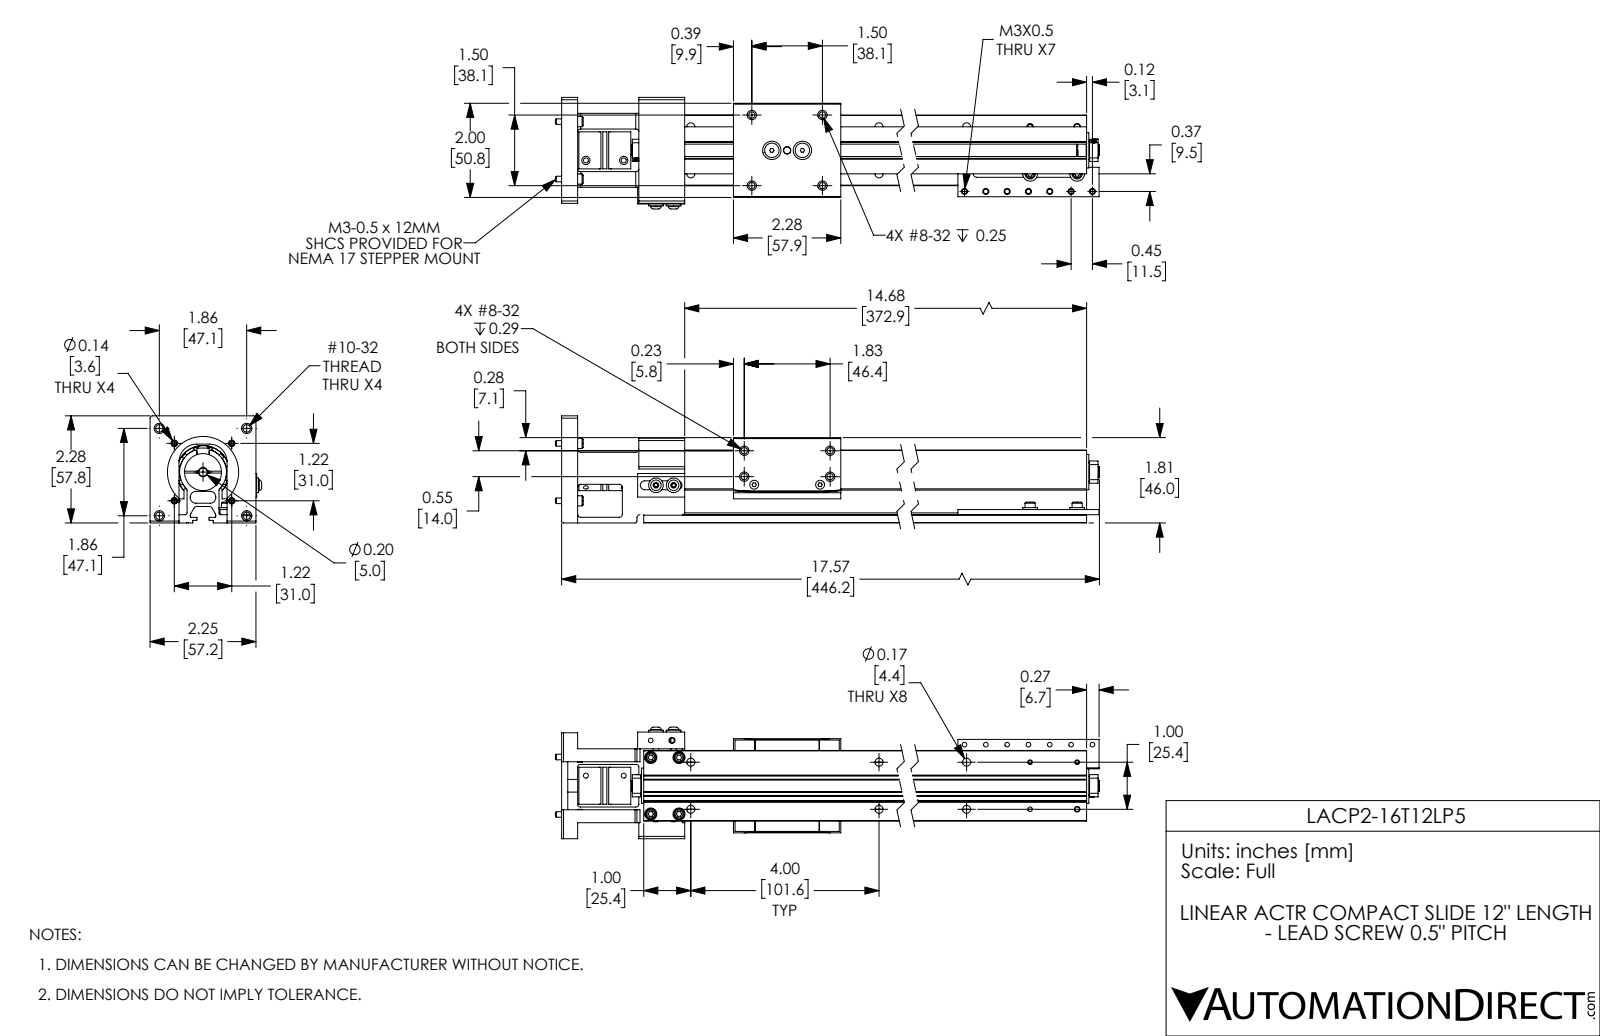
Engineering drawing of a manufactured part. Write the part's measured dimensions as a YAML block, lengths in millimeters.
part_name: "LACP2-16T12LP5; LACP2-16T12LP5_BLOCK; LACP2-16T12LP5_BODY"
step_written_by: "SolidWorks 2017 (AUTOMOTIVE_DESIGN)"
units: millimeters
bodies: {solids: 46, faces: 1240, planar: 502, cylindrical: 469, other: 269}
overall_size: [449.6, 60.2, 57.8]
volume: 316800
surface_area: 188700
round_holes:
  - {diameter: 2.5, count: 18}
  - {diameter: 3.5, count: 10}
  - {diameter: 4.4, count: 8}
  - {diameter: 3.6, count: 4}
  - {diameter: 3.7, count: 4}
  - {diameter: 4, count: 4}
  - {diameter: 6.5, count: 4}
  - {diameter: 2.5, count: 2}
  - {diameter: 2.7, count: 2}
  - {diameter: 3, count: 2}
  - {diameter: 3.2, count: 2}
  - {diameter: 3.2, count: 2}
round_bosses_or_shafts:
  - {diameter: 5.5, count: 10}
  - {diameter: 3, count: 10}
  - {diameter: 7.9, count: 4}
  - {diameter: 3, count: 3}
  - {diameter: 7.8, count: 2}
  - {diameter: 5.7, count: 2}
  - {diameter: 4.2, count: 2}
  - {diameter: 3.5, count: 2}
partial_cylinders:
  - {radius: 0.3, count: 17}
  - {radius: 1.3, count: 9}
  - {radius: 1, count: 8}
  - {radius: 1.7, count: 7}
  - {radius: 0.5, count: 4}
  - {radius: 1.9, count: 4}
  - {radius: 2, count: 4}
  - {radius: 3, count: 4}
face_to_face_distances: [4.4, 17.2, 8.6, 4.4, 39, 4.3, 21.6, 6.1, 10.4, 27.7]
hole_center_spacings: [25.4, 30.5, 11.5, 21.9, 23, 28.7, 33.3, 39.9]
